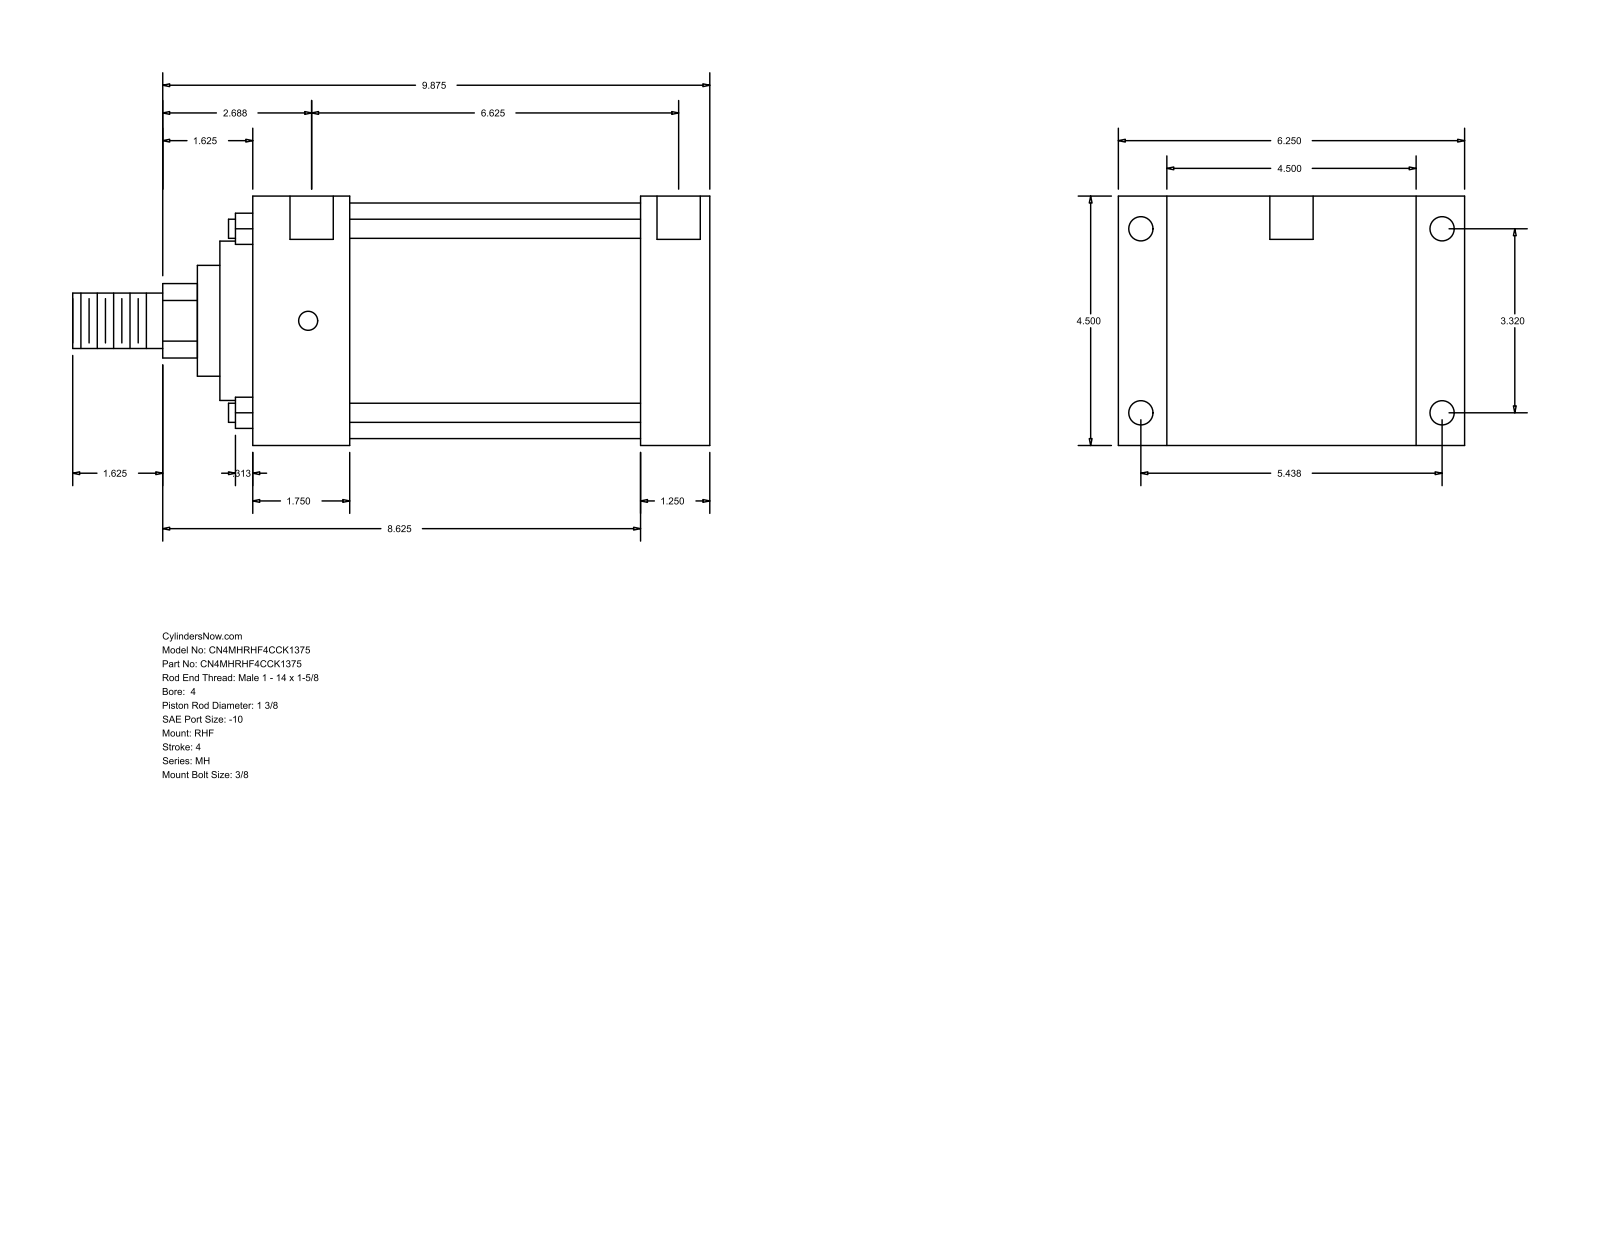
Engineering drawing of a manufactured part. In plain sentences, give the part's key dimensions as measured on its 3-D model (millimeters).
The part is named "MH_RHF__0400_1.375". Its 3-D file was written by "GSSL Pune (CONFIG_CONTROL_DESIGN)". It is 0 solids with 90 faces: 61 planar, 29 cylindrical and 0 other. Overall it measures 292.1 by 158.75 by 114.3 millimeters. Round holes: 4 of diameter 8.73, 4 of diameter 11.13, 2 of diameter 19.84. Round bosses or shafts: 4 of diameter 8.76, 1 of diameter 107.95, 1 of diameter 73.03, 1 of diameter 50.8, 1 of diameter 34.92, 1 of diameter 25.4. Partial cylindrical surfaces (rounded edges, fillets, slot ends): 1 of radius 17.06. The main face-to-face distances are 114.3, 31.75, 177.8, 209.55, 22.23, 136.53, 44.45, 133.35, 165.1, 158.76. The hole center spacings are 84.32, 138.12, 161.82, 171.45, 1.58, 1.59, 168.28, 169.86.
